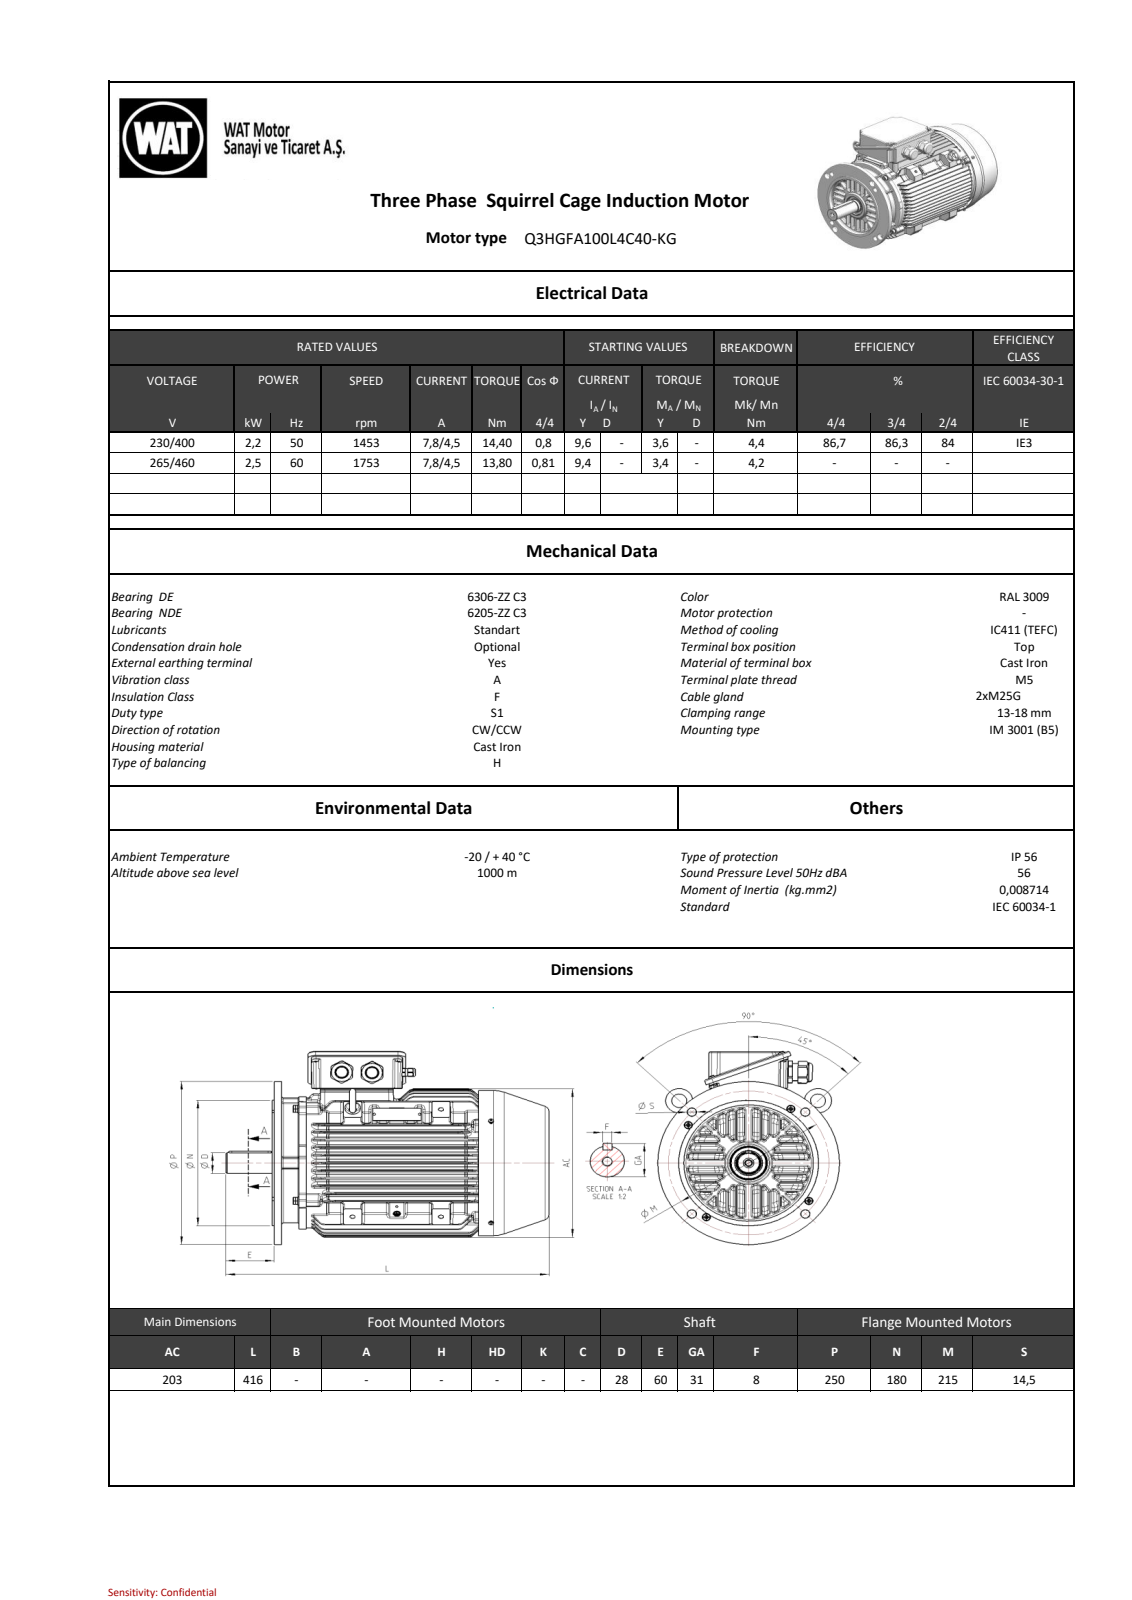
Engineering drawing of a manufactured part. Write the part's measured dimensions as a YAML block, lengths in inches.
part_name: "C901B52CA9A90a2v"
step_written_by: "SIEMENS PLM Software NX 11.0 (AUTOMOTIVE_DESIGN)"
units: inches
bodies: {solids: 0, faces: 4109, planar: 801, cylindrical: 1006, other: 2302}
overall_size: [16.378, 11.436, 9.843]
round_holes:
  - {diameter: 0.197, count: 8}
  - {diameter: 0.268, count: 6}
  - {diameter: 0.394, count: 6}
  - {diameter: 0.433, count: 4}
  - {diameter: 0.165, count: 2}
  - {diameter: 0.677, count: 2}
  - {diameter: 0.256, count: 1}
  - {diameter: 0.276, count: 1}
  - {diameter: 0.335, count: 1}
  - {diameter: 0.413, count: 1}
  - {diameter: 0.551, count: 1}
  - {diameter: 0.571, count: 1}
round_bosses_or_shafts:
  - {diameter: 0.394, count: 4}
  - {diameter: 0.341, count: 4}
  - {diameter: 0.315, count: 4}
  - {diameter: 0.984, count: 3}
  - {diameter: 0.157, count: 3}
  - {diameter: 1.091, count: 2}
  - {diameter: 0.994, count: 2}
  - {diameter: 0.787, count: 2}
partial_cylinders:
  - {radius: 0.157, count: 240}
  - {radius: 0.059, count: 117}
  - {radius: 0.118, count: 67}
  - {radius: 0.079, count: 31}
  - {radius: 0.071, count: 23}
  - {radius: 0.039, count: 21}
  - {radius: 0.01, count: 17}
  - {radius: 1.043, count: 12}
face_to_face_distances: [0.533, 1.069, 0.536, 0.197, 1.608, 1.075, 0.539, 3.104, 2.028, 2.567]
hole_center_spacings: [3.524, 4.983, 2.303, 2.815, 1.223, 4.043, 5.118, 5.772]
